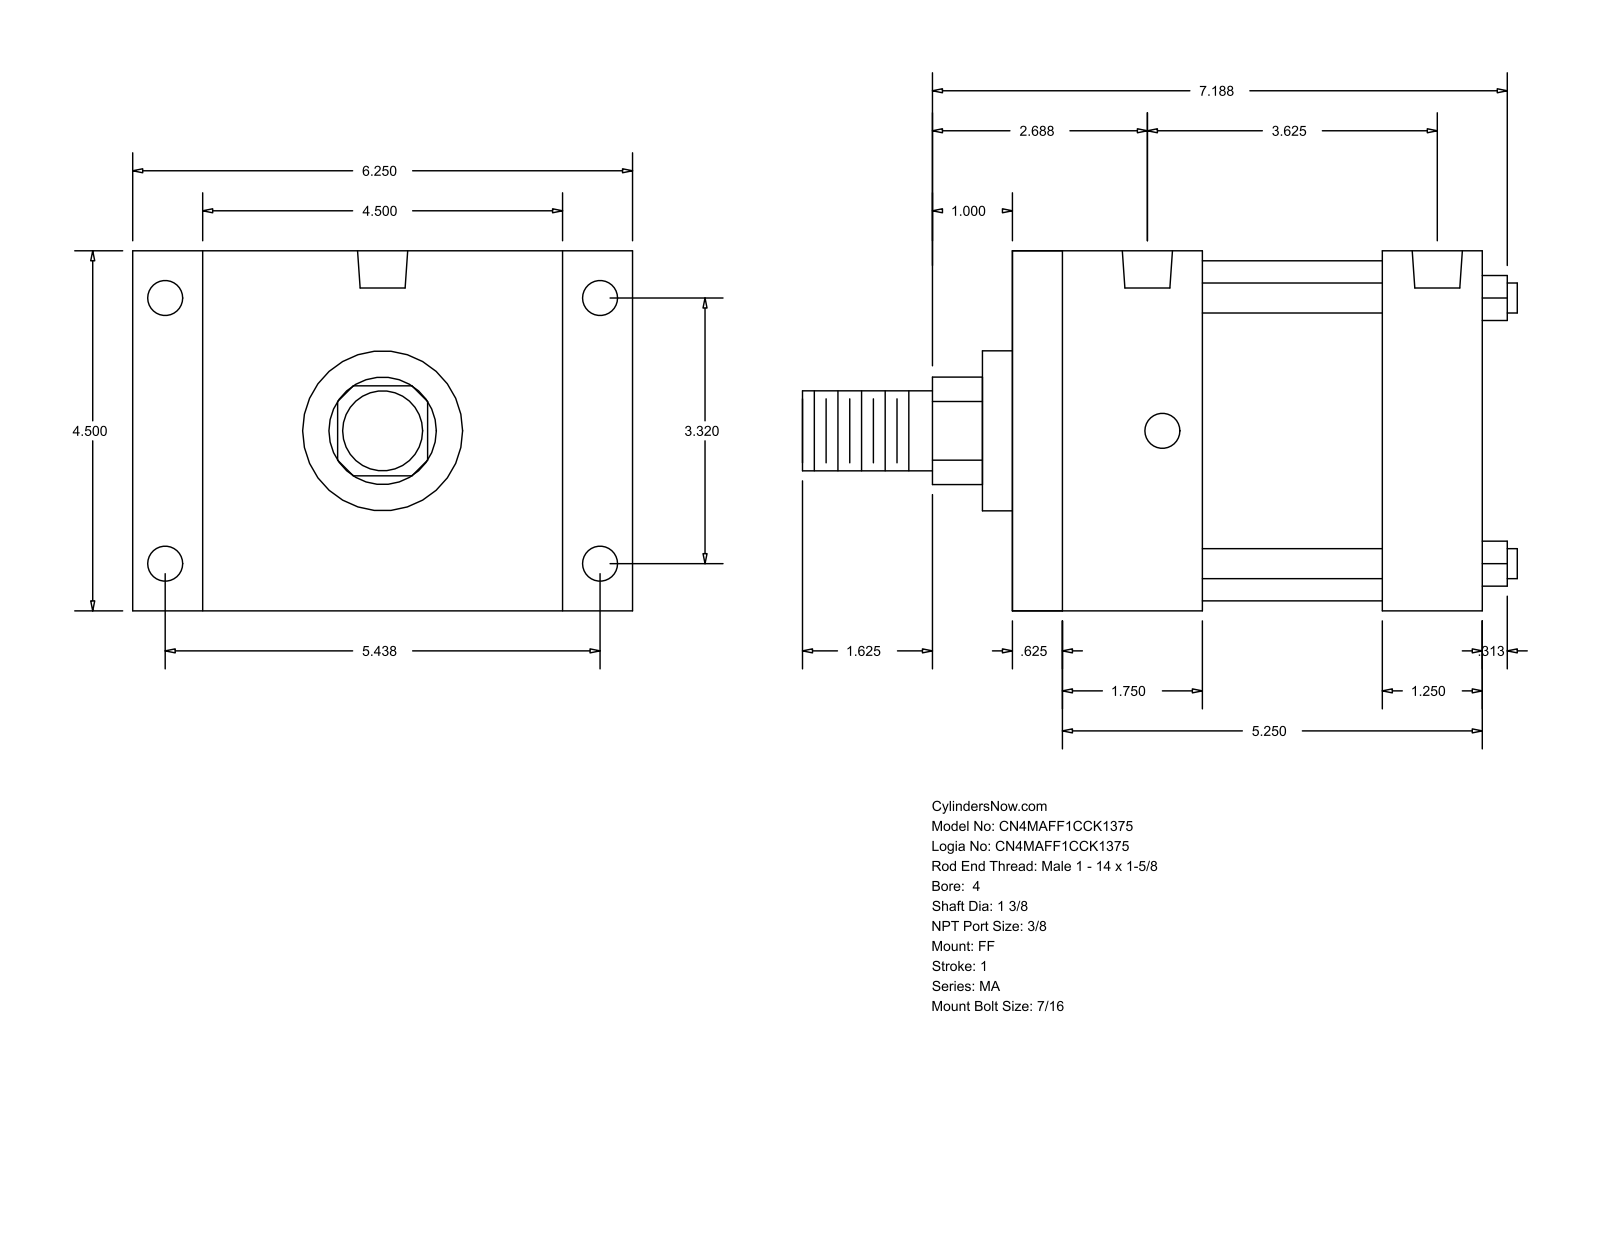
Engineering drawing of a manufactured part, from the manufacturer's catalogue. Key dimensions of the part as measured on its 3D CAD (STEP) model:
Part name (STEP PRODUCT): MA_FF__0400_1.375
STEP written by: GSSL Pune (CONFIG_CONTROL_DESIGN)
Units: millimetres
Bodies: 0 solids, 92 faces (64 planar, 28 cylindrical, 0 other)
Overall size (bounding box): 227.01 × 158.75 × 114.3
Round holes (diameter × count): ⌀11.11 ×8, ⌀15.93 ×2
Round bosses / shafts (diameter × count): ⌀9.53 ×4, ⌀107.95 ×1, ⌀50.8 ×1, ⌀34.92 ×1, ⌀25.4 ×1
Partial cylindrical surfaces — rounded edges, fillets, slot ends (radius × count): R17.06 ×1
Main face-to-face distances: 114.3, 149.22, 15.87, 133.35, 22.23, 136.53, 117.48, 101.61, 31.74, 60.32
Hole centre spacings: 4.77, 82.54, 84.32, 87.31, 138.12, 161.82, 92.08
